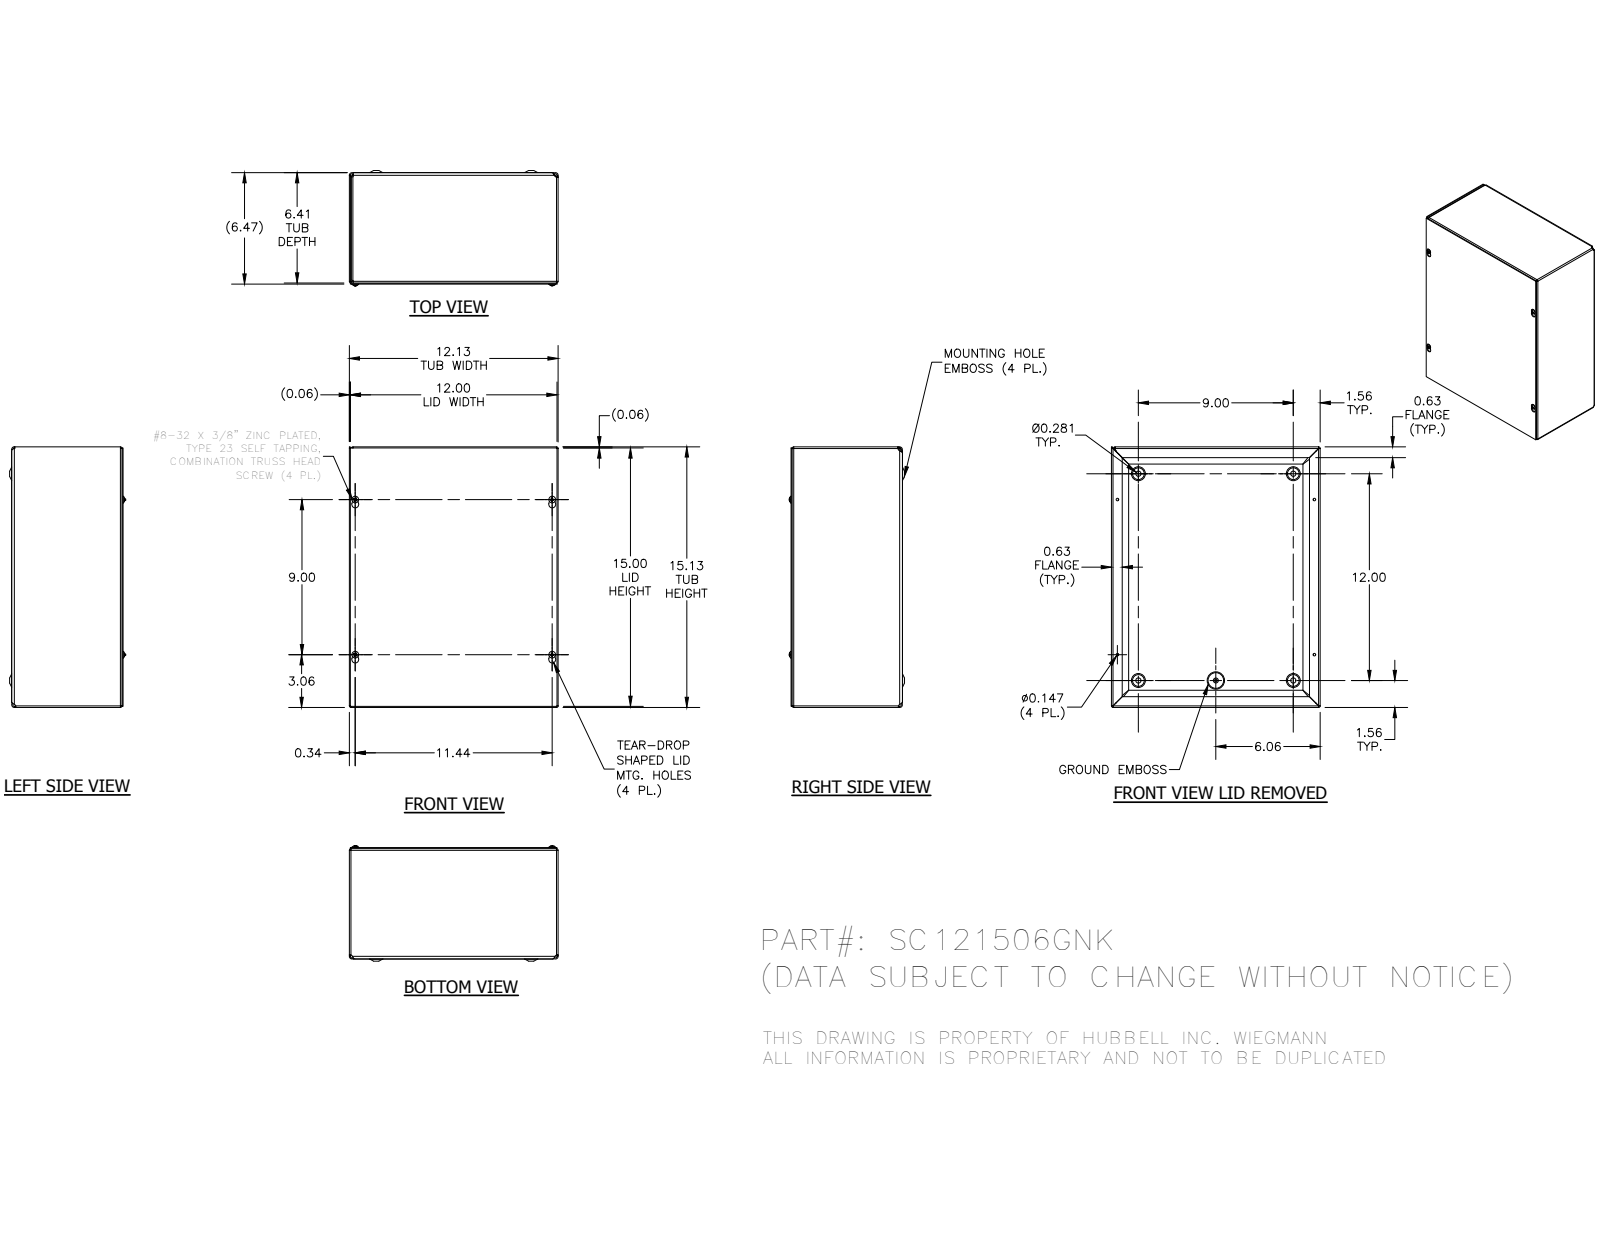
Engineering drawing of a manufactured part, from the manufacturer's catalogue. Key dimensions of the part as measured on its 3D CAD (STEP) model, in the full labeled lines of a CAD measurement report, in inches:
Part name (STEP PRODUCT): SC1215GNKBKP; SC121506GNKWRA; SC1215GNKLID; 34056 (+1 more)
STEP written by: Autodesk Inventor 2014 (AUTOMOTIVE_DESIGN)
Units: inches
Bodies: 7 solids, 358 faces (133 planar, 73 cylindrical, 152 other)
Overall size (bounding box): 15.125 × 12.125 × 6.693
Volume: 48 in³ · Surface area: 1 562 in²
Round holes (diameter × count): ⌀0.147 ×4, ⌀0.3 ×4, ⌀0.165 ×1
Round bosses / shafts (diameter × count): ⌀0.384 ×4, ⌀0.164 ×4, ⌀0.228 ×1
Partial cylindrical surfaces — rounded edges, fillets, slot ends (radius × count): R0.031 ×8, R0.093 ×8, R0.055 ×4, R0.062 ×4, R0.094 ×4, R0.117 ×4, R0.124 ×4, R0.125 ×4
Main face-to-face distances: 0.062, 6.343, 6.405, 0.063, 6.406, 6.468, 15.063, 0.062, 12.125, 12.063
Hole centre spacings: 9, 4.5, 10.328, 10.328, 10.57, 10.571, 11.437, 12
